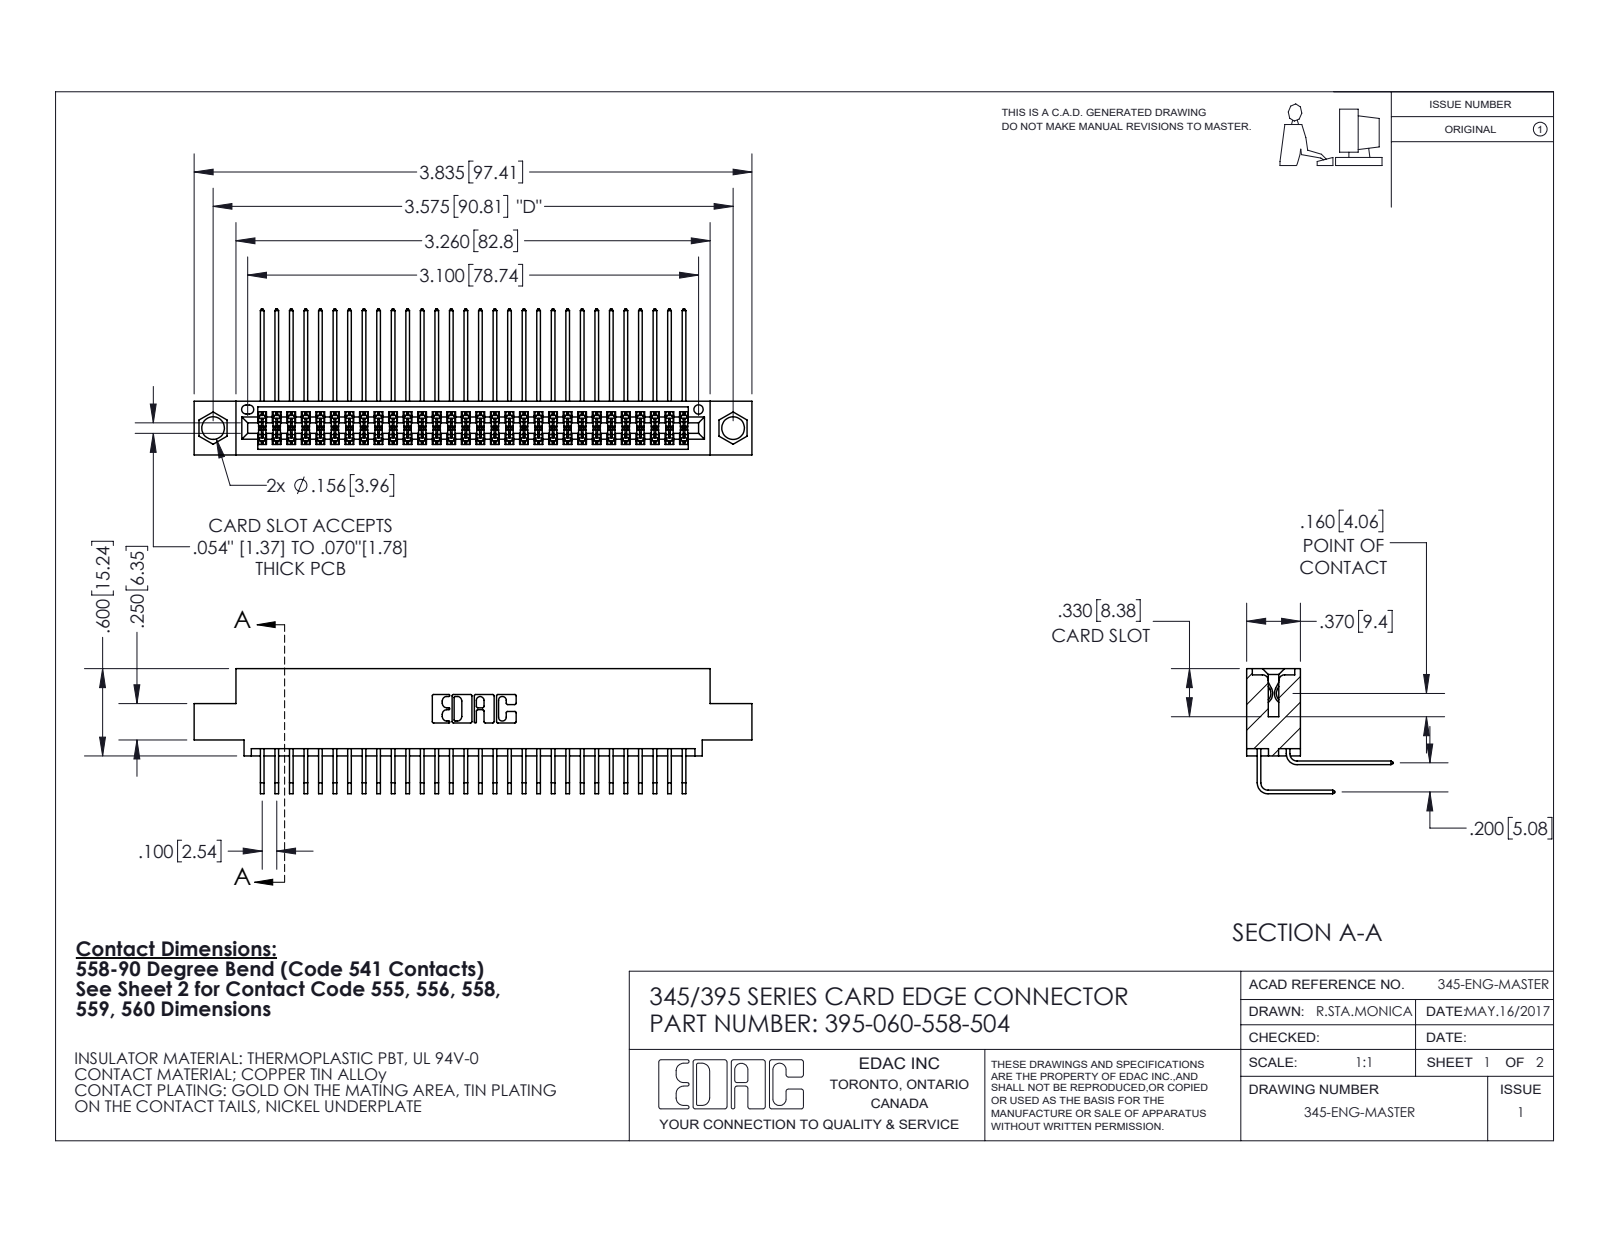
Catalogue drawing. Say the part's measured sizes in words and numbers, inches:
The part is named "395-060-558-504; 345 Part_0.110 Offset - 0.156 Dia-TI; 345-292-001_558 559 Tail - 1; 345-292-001_558 Tail - 2". Its 3-D file was written by "SolidWorks 2020 (CONFIG_CONTROL_DESIGN)". It is 61 solids with 3264 faces: 2198 planar, 1066 cylindrical and 0 other. Overall it measures 3.835 by 1.005 by 0.859 inches. Its volume is 0.581 cubic inches and its surface area 23.88 square inches. Round holes: 2 of diameter 0.156, 1 of diameter 0.064. Partial cylindrical surfaces (rounded edges, fillets, slot ends): 91 of radius 0.006, 22 of radius 0.01, 6 of radius 0.007, 6 of radius 0.031, 3 of radius 0.026, 2 of radius 0.014, 2 of radius 0.019, 2 of radius 0.022. The main face-to-face distances are 0.072, 0.298, 0.2, 0.37, 0.098, 0.272, 0.025, 0.225, 0.025, 0.175. The hole center spacings are 0.27, 3.34, 3.575.
